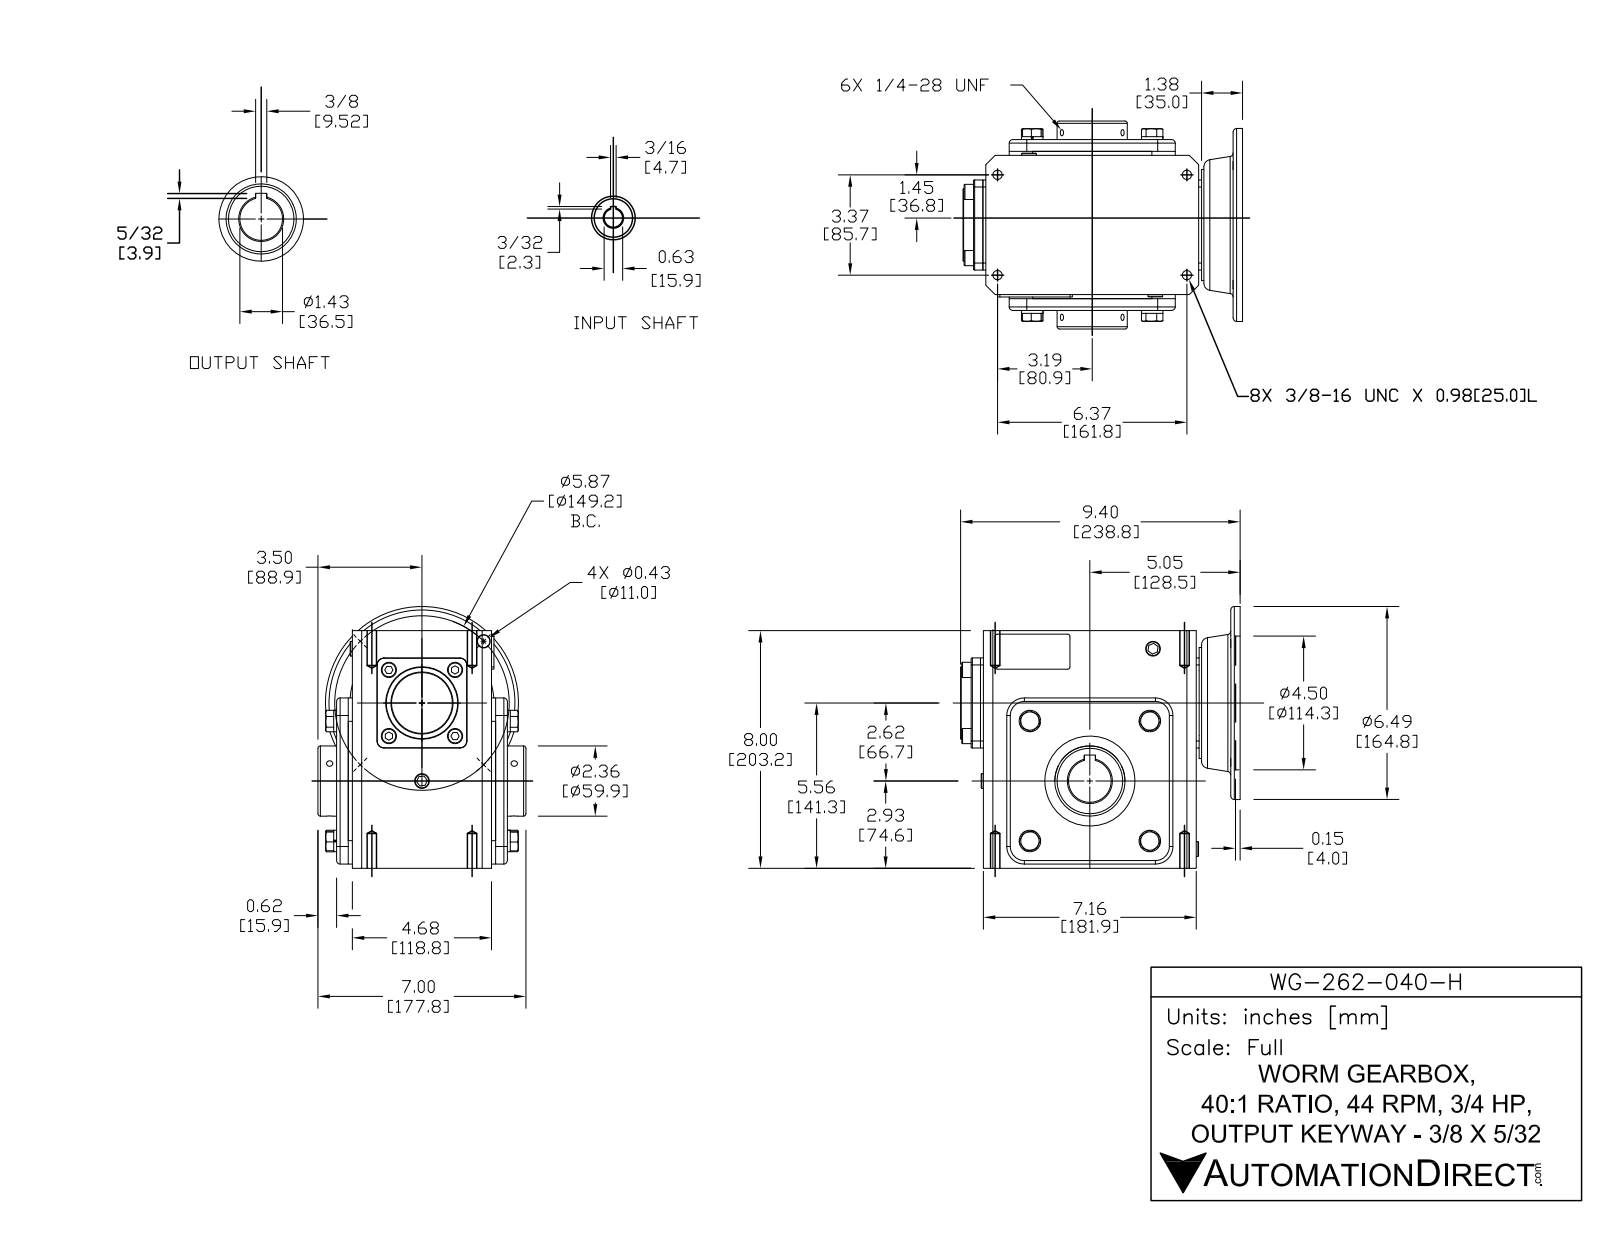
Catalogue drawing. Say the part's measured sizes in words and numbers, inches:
The part is named "WG-262-040-H". Its 3-D file was written by "SolidWorks 2015 (CONFIG_CONTROL_DESIGN)". It is 37 solids with 558 faces: 306 planar, 156 cylindrical and 96 other. Overall it measures 9.409 by 8.811 by 7 inches. Its volume is 310.4 cubic inches and its surface area 663.9 square inches. Round holes: 6 of diameter 0.213, 4 of diameter 0.313, 4 of diameter 0.406, 1 of diameter 0.591, 1 of diameter 0.625, 1 of diameter 1.437, 1 of diameter 1.457, 1 of diameter 2.362, 1 of diameter 3.031, 1 of diameter 3.819, 1 of diameter 4.5. Round bosses or shafts: 4 of diameter 0.724, 4 of diameter 0.512, 1 of diameter 6.496, 1 of diameter 3.74, 1 of diameter 2.441, 1 of diameter 2.047, 1 of diameter 1.181, 1 of diameter 1.142. Partial cylindrical surfaces (rounded edges, fillets, slot ends): 8 of radius 0.079, 8 of radius 0.118, 4 of radius 0.236, 4 of radius 0.591, 4 of radius 0.787, 2 of radius 0.02, 2 of radius 0.039. The main face-to-face distances are 4.961, 0.394, 0.098, 5.217, 5.354, 0.138, 4.823, 0.531, 7.264, 8. The hole center spacings are 2.937, 3.489, 4.154, 5.757, 6.213, 2.148, 3.375, 5.14.
